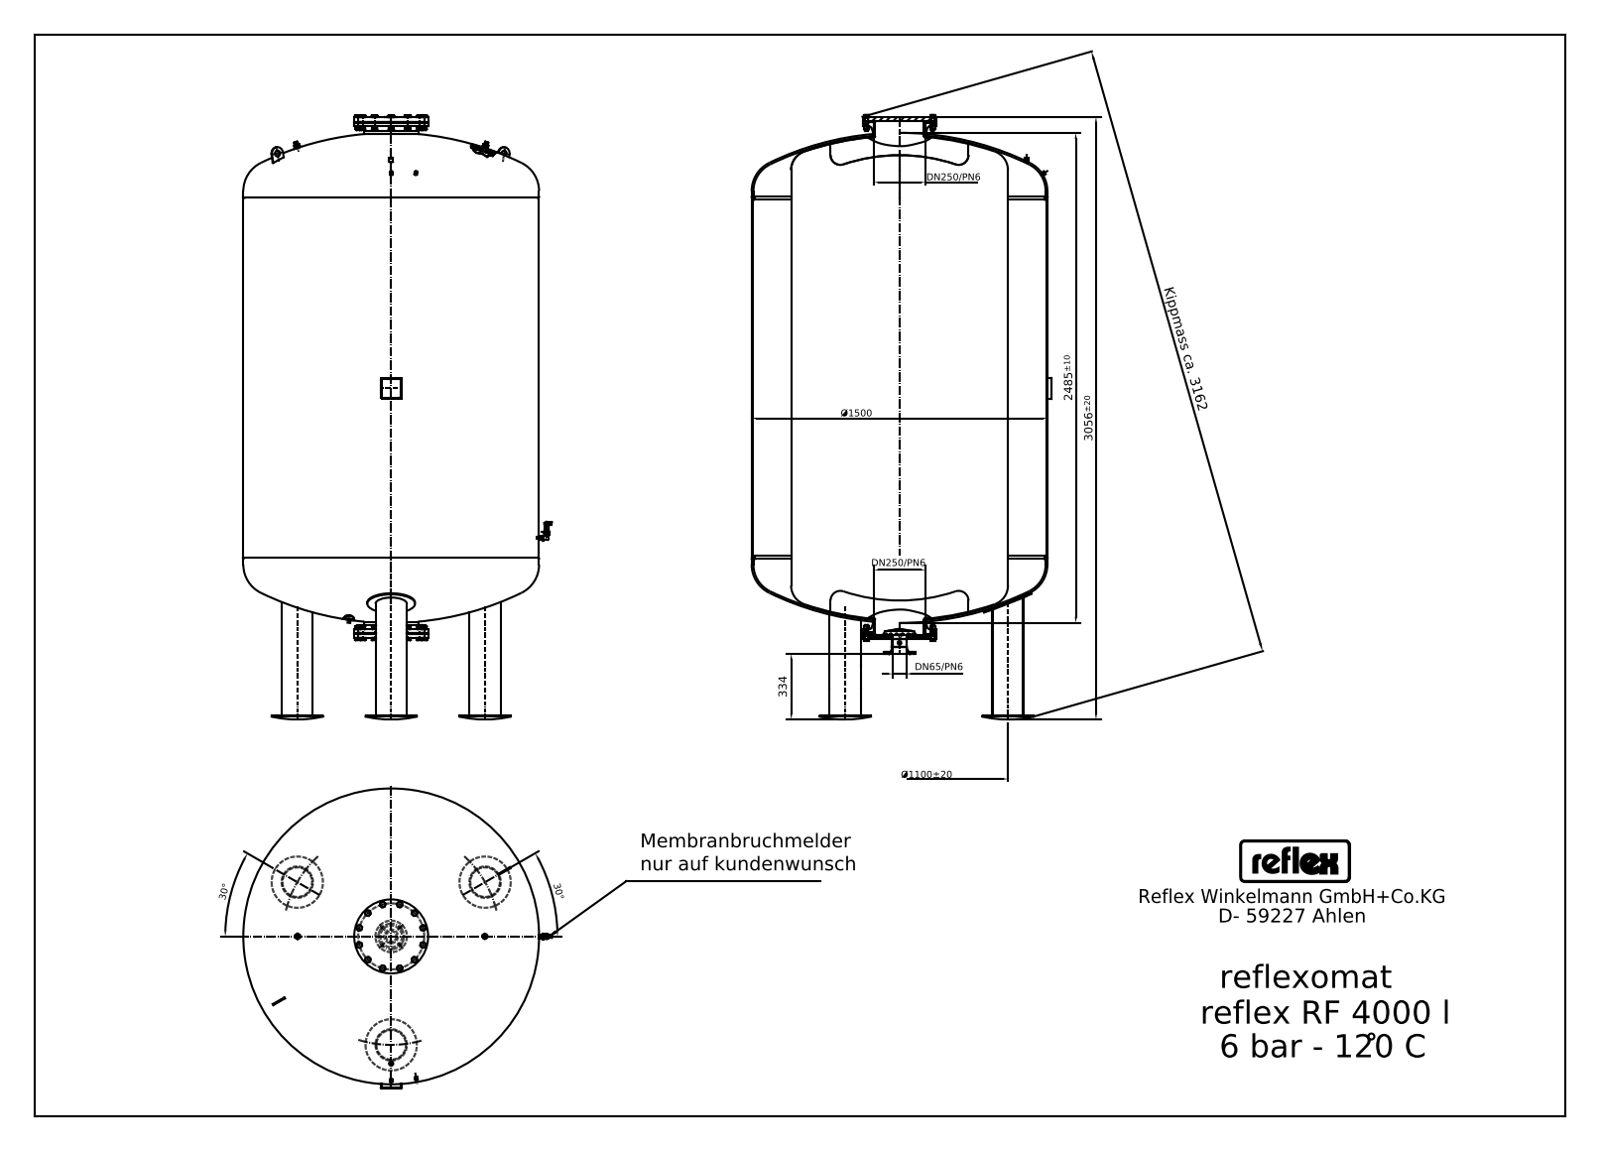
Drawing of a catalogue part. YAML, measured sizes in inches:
step_written_by: "Mechanical Desktop 2009 (CONFIG_CONTROL_DESIGN)"
units: inches
bodies: {solids: 23, faces: 889, planar: 514, cylindrical: 207, other: 168}
overall_size: [120.669, 61.654, 59.843]
volume: 248900
surface_area: 35670
round_holes:
  - {diameter: 0.451, count: 2}
  - {diameter: 0.138, count: 1}
  - {diameter: 0.589, count: 1}
  - {diameter: 1.181, count: 1}
  - {diameter: 10.252, count: 1}
round_bosses_or_shafts:
  - {diameter: 0.63, count: 12}
  - {diameter: 6.26, count: 3}
  - {diameter: 0.839, count: 3}
  - {diameter: 0.728, count: 3}
  - {diameter: 1.102, count: 2}
  - {diameter: 0.787, count: 2}
  - {diameter: 59.055, count: 1}
  - {diameter: 14.764, count: 1}
partial_cylinders:
  - {radius: 0.039, count: 5}
  - {radius: 0.332, count: 4}
  - {radius: 0.133, count: 3}
  - {radius: 0.236, count: 3}
  - {radius: 0.079, count: 2}
  - {radius: 0.118, count: 2}
  - {radius: 0.227, count: 2}
  - {radius: 0.398, count: 2}
face_to_face_distances: [71.85, 0.866, 103.15, 1.063, 102.087, 15.118, 87.165, 15.315, 88.031, 16.181]
hole_center_spacings: [25.394, 30.295, 39.53]
